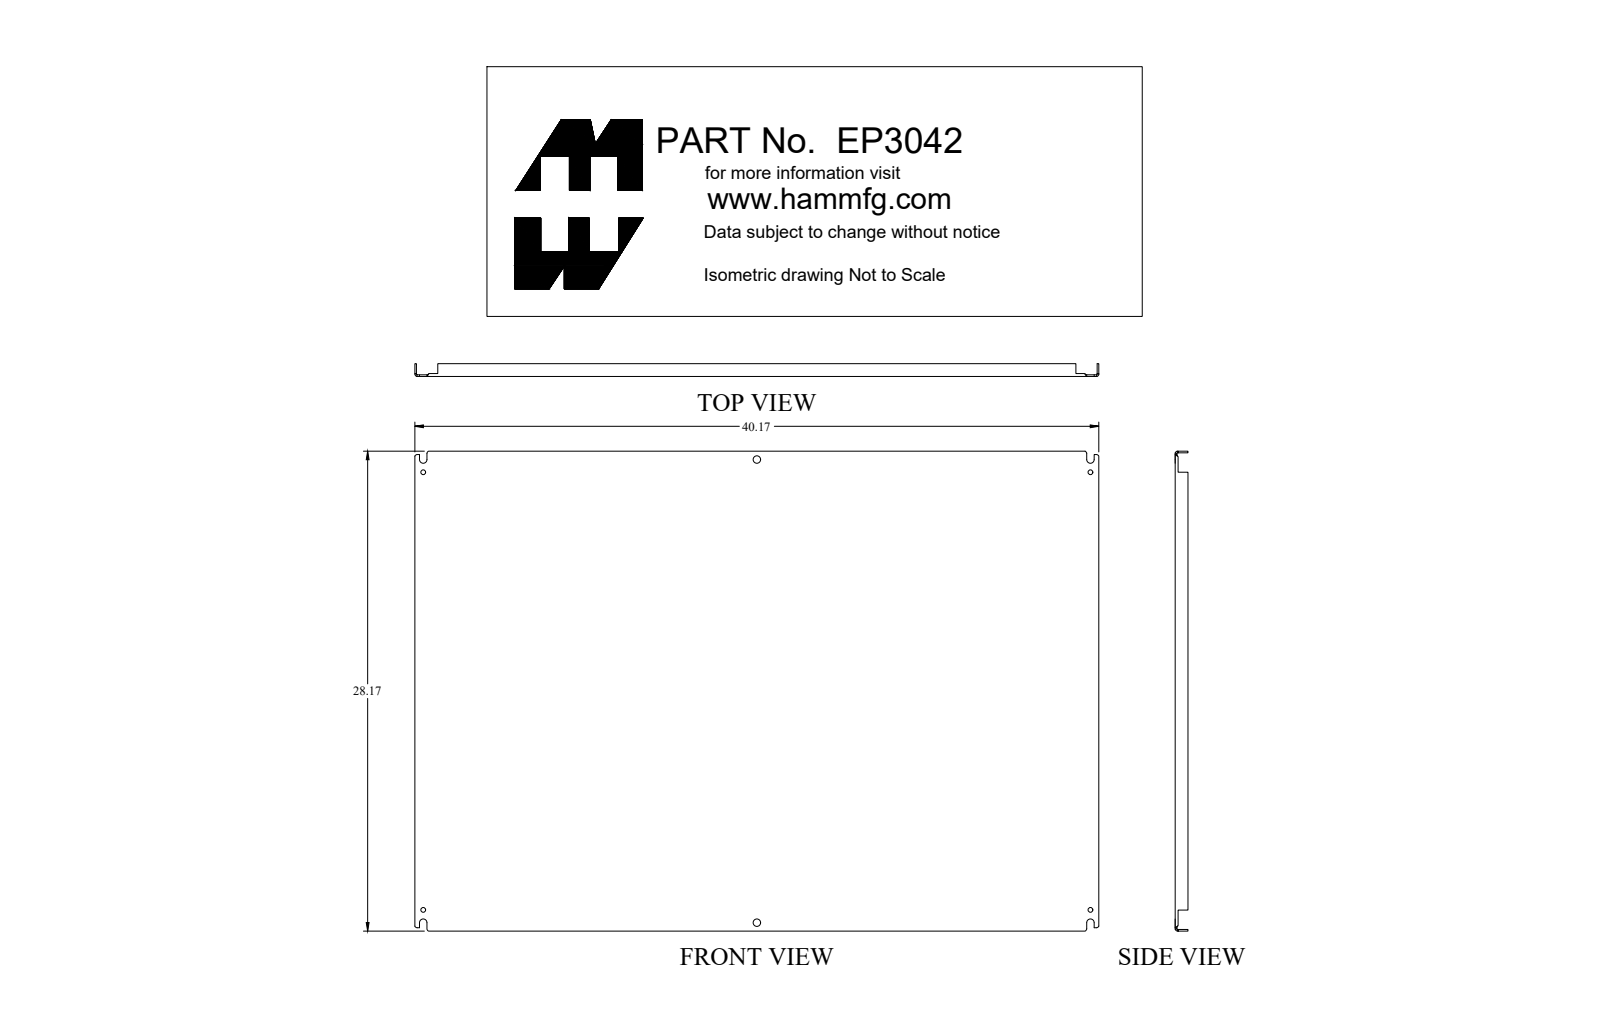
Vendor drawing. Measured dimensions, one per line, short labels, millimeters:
name: EP3042
written by: SolidWorks 2018 (AUTOMOTIVE_DESIGN)
unit: mm
bodies: 1 solid, 132 faces (74 planar, 42 cylindrical, 16 other)
size: 1020.3 × 715.5 × 19.1
volume: 1 880 000 mm³; area: 1 567 000 mm²
holes: 4× ⌀7.1, 2× ⌀11.1
rounds: 4× R1.2, 4× R1.6, 4× R3.6, 4× R5.6
face distances: 2.4, 713.1, 1017.9, 715.5, 710.7, 1015.5, 1020.3, 19.1, 16.6, 4.3
hole spacings: 498, 835.8, 652.5, 995.4, 1190.2, 690.6
